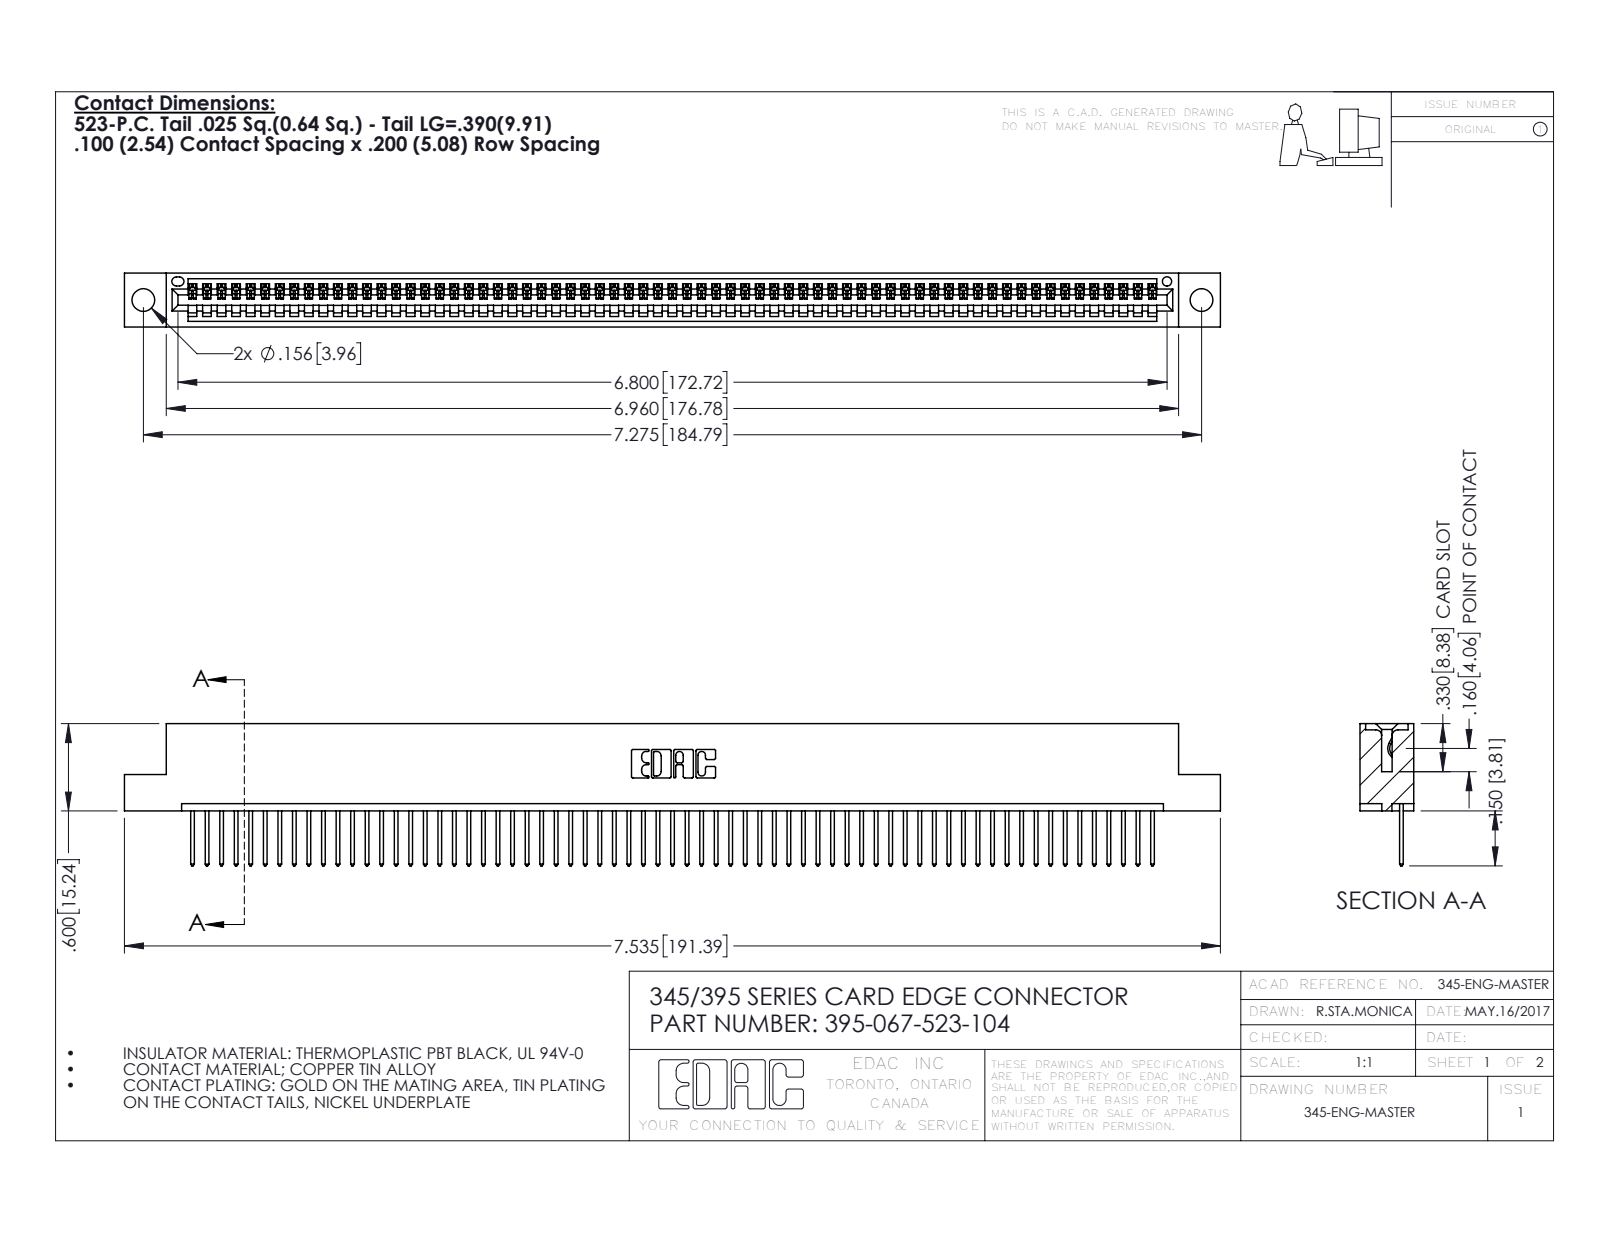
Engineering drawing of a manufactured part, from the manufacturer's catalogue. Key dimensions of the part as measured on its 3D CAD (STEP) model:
Part name (STEP PRODUCT): 345-292-001_345-293-123; 345 Part_Flush Mounting Lugs - 0.156 Dia-TH; 395-067-523-104
STEP written by: SolidWorks 2016 (CONFIG_CONTROL_DESIGN)
Units: inches
Bodies: 68 solids, 4012 faces (2760 planar, 1252 cylindrical, 0 other)
Overall size (bounding box): 7.535 × 0.977 × 0.37
Volume: 1.115 in³ · Surface area: 37.97 in²
Round holes (diameter × count): ⌀0.156 ×2, ⌀0.064 ×1
Partial cylindrical surfaces — rounded edges, fillets, slot ends (radius × count): R0.006 ×134, R0.01 ×134, R0.01 ×22, R0.007 ×6, R0.031 ×6, R0.026 ×3, R0.031 ×2, R0.04 ×2
Main face-to-face distances: 0.298, 0.072, 0.37, 0.2, 0.098, 0.272, 0.025, 0.225, 0.149, 0.072
Hole centre spacings: 0.27, 7.039, 7.275
